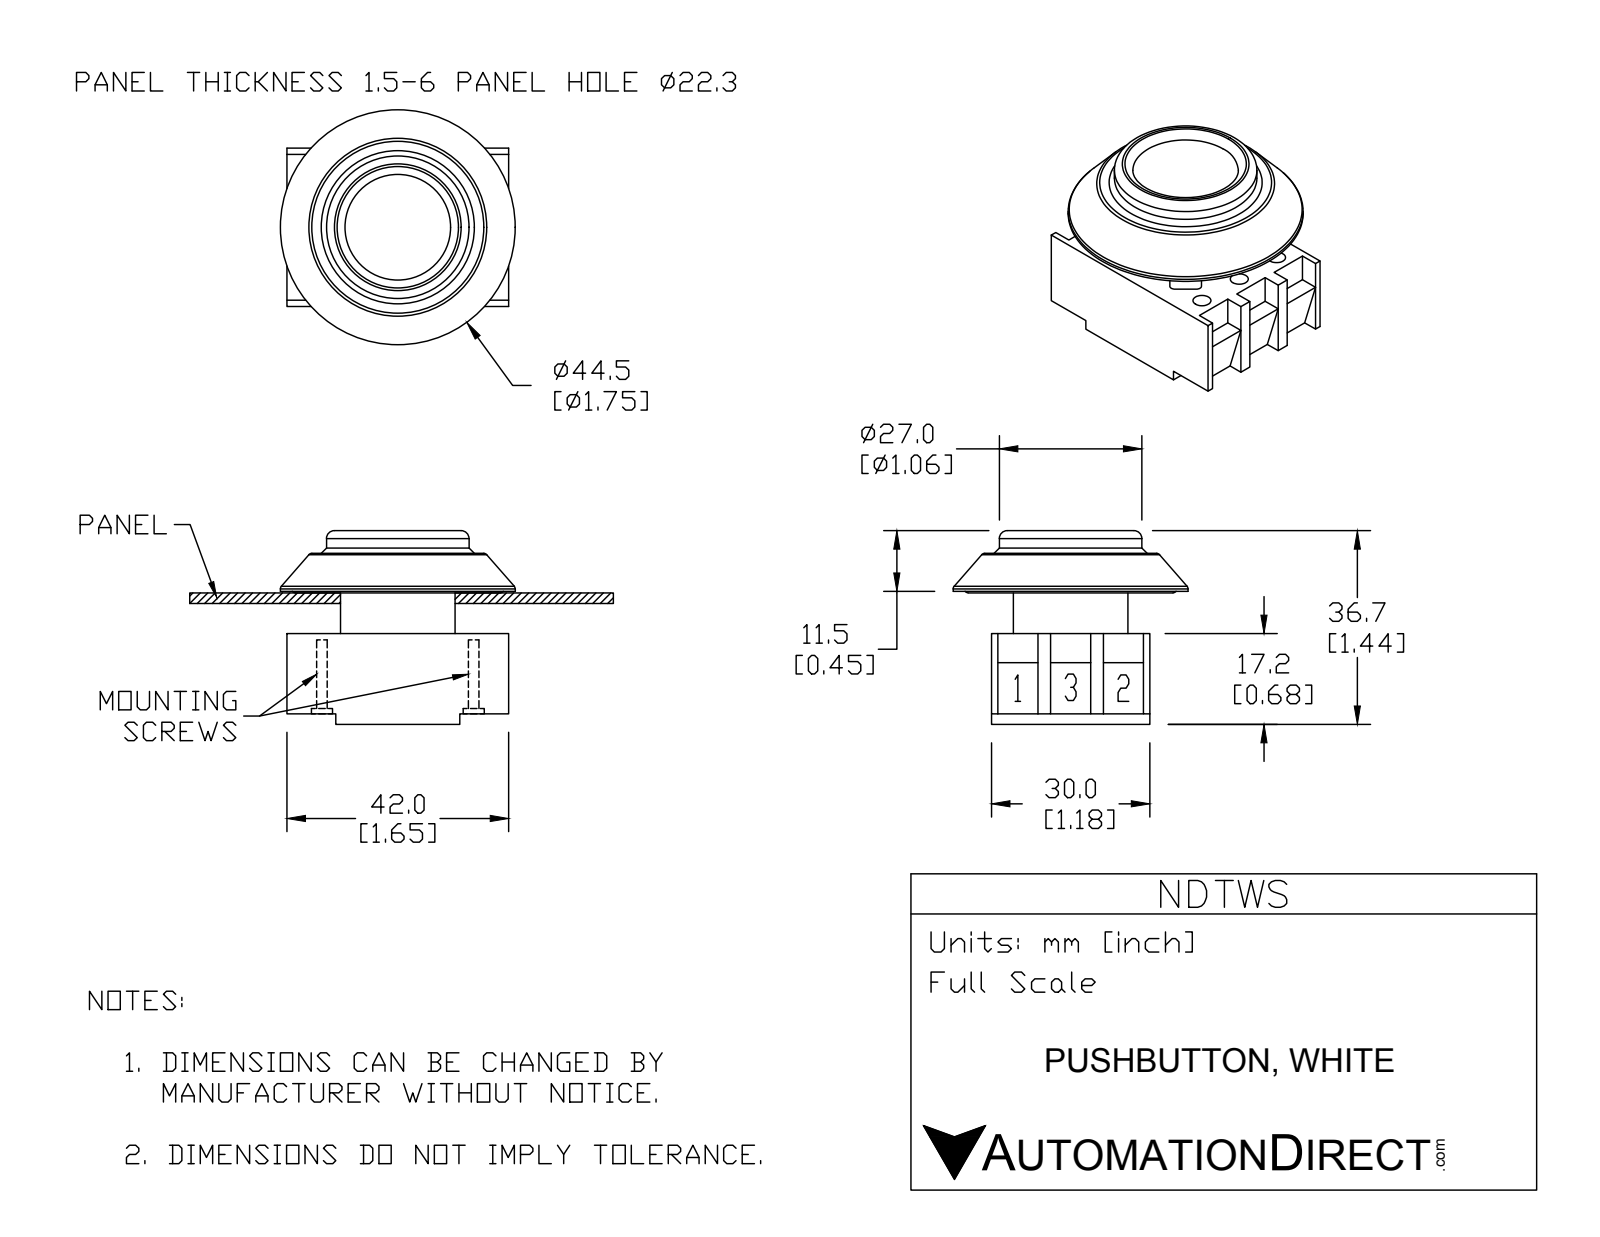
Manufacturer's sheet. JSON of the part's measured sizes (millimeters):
{"part_name": "NDTWS", "step_written_by": "SolidWorks 2015 (AUTOMOTIVE_DESIGN)", "units": "millimeters", "bodies": {"solids": 7, "faces": 217, "planar": 127, "cylindrical": 65, "other": 25}, "overall_size": [44.5, 44.5, 36.7], "volume_mm3": 25120, "surface_area_mm2": 16719, "round_holes": [[3.4, 6], [5, 6], [12.5, 1]], "round_bosses_or_shafts": [[4.6, 2], [4, 2], [44.5, 1], [27, 1], [21.7, 1]], "partial_cylinders_radius": [[1, 8], [8.7, 5], [11, 1]], "face_to_face_distances": [7.2, 15.2, 30, 10, 8, 7.5, 7.7, 10.3, 18, 23.2], "hole_center_spacings": [10, 17.52, 30.45, 28.76, 14.38, 20, 35.03]}
